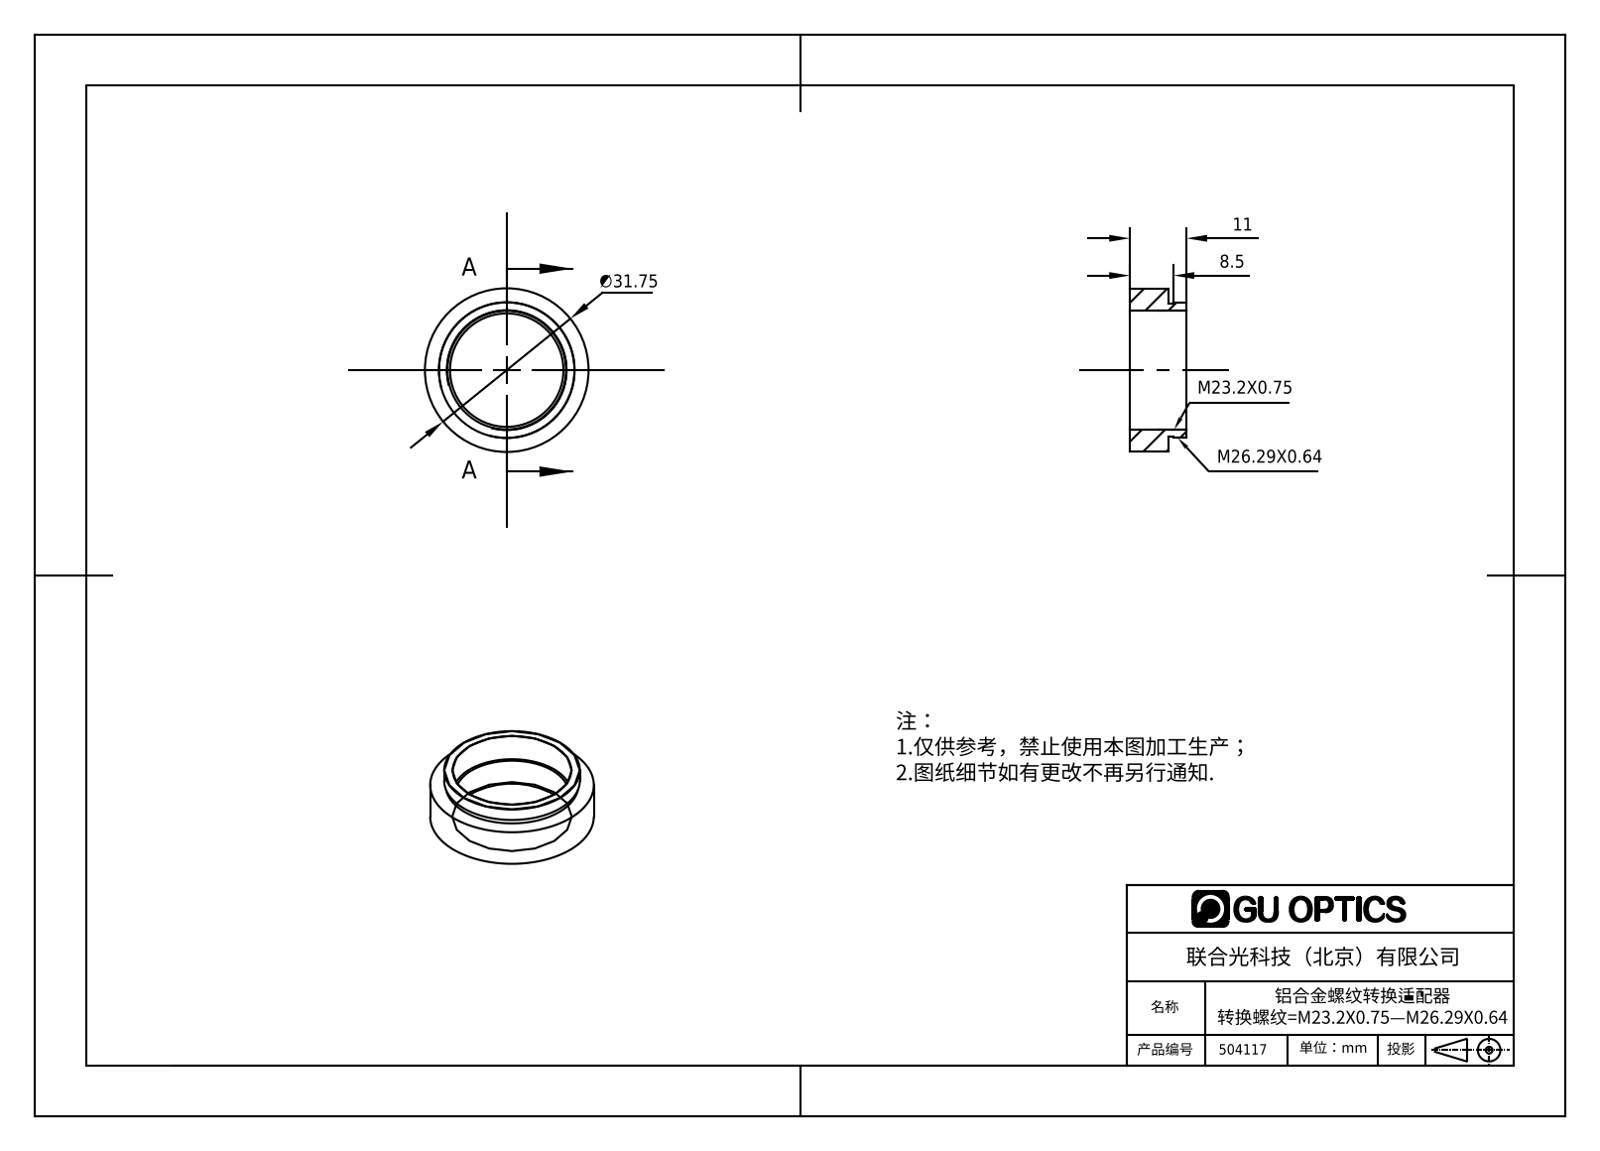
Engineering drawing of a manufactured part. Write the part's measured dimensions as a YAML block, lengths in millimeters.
part_name: "504117"
step_written_by: "SolidWorks 2016 (AUTOMOTIVE_DESIGN)"
units: millimeters
bodies: {solids: 1, faces: 15, planar: 5, cylindrical: 10, other: 0}
overall_size: [31.75, 31.75, 11]
volume: 3445
surface_area: 2679
round_holes:
  - {diameter: 22, count: 1}
  - {diameter: 23, count: 1}
round_bosses_or_shafts:
  - {diameter: 31.75, count: 1}
  - {diameter: 26.32, count: 1}
  - {diameter: 25.8, count: 1}
face_to_face_distances: [7.5, 11, 3.5, 5.5, 2, 8.5, 3, 1, 2.5]
